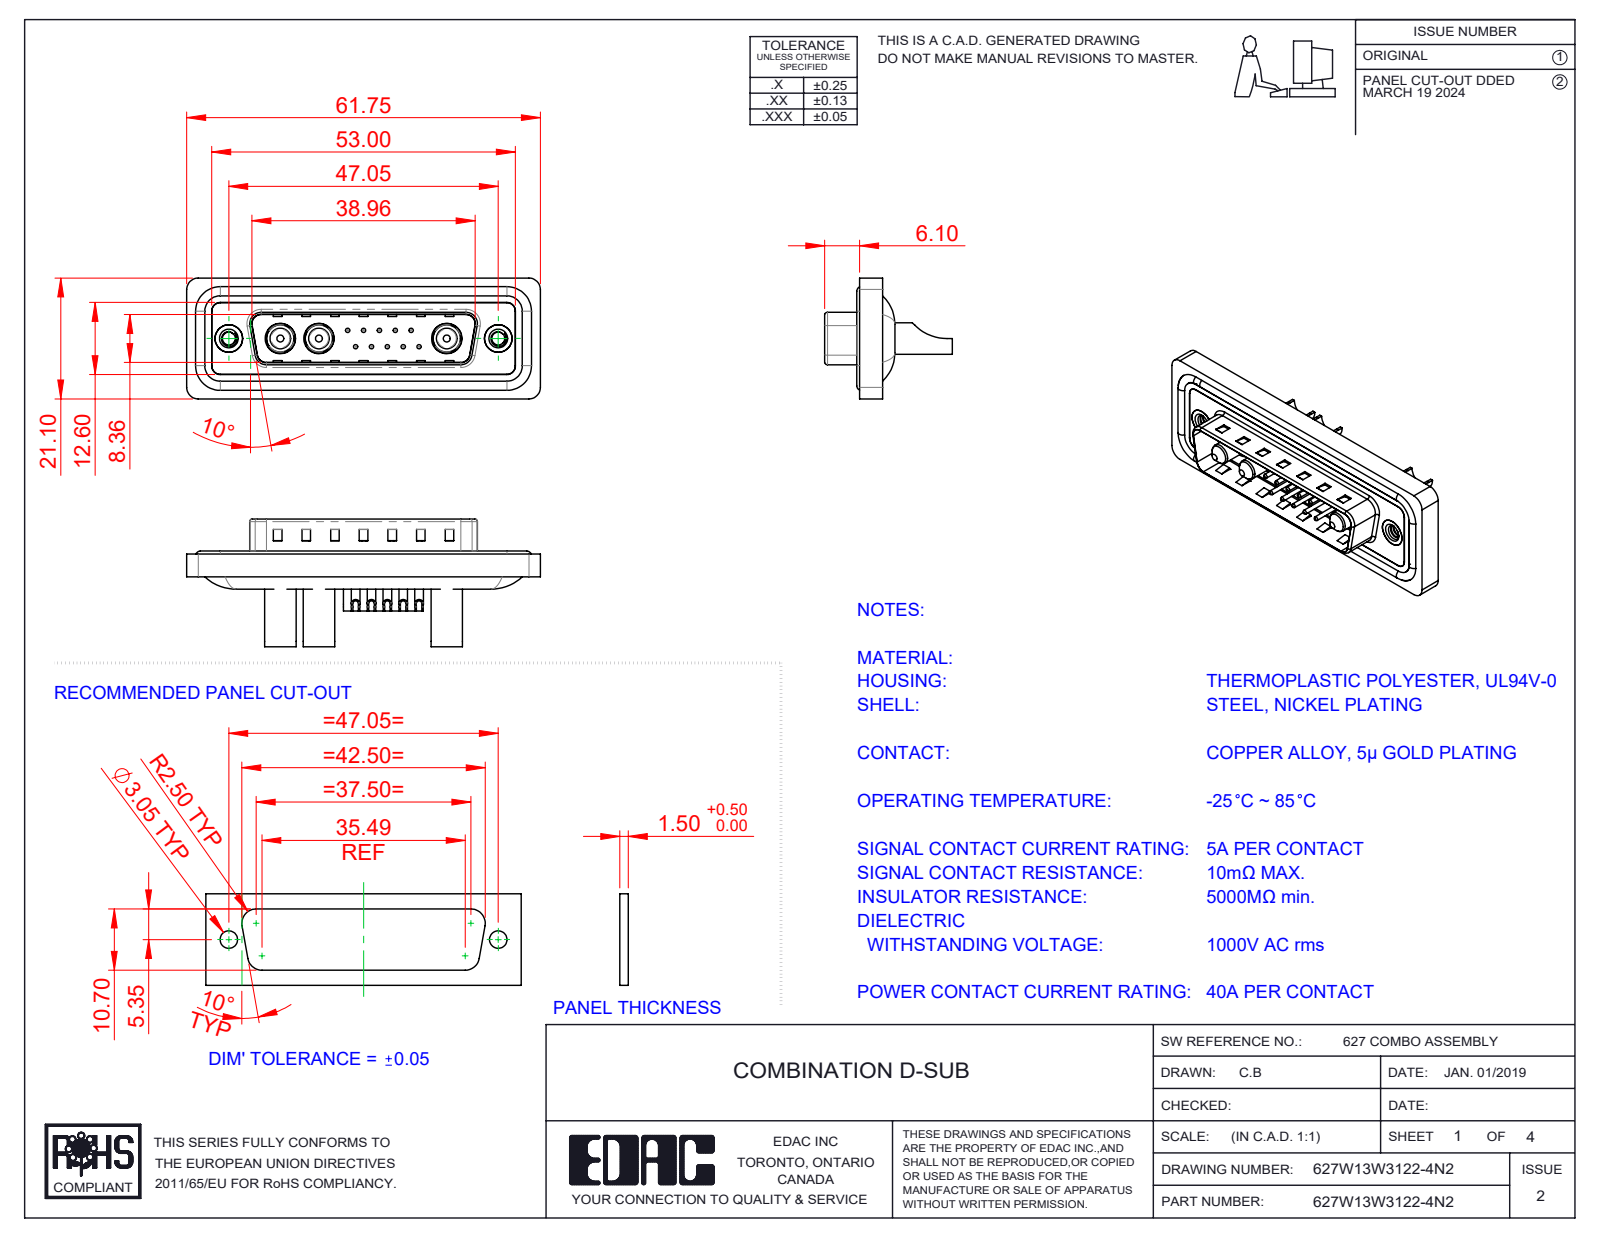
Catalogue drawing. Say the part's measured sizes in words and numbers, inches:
The part is named "627W13W3122-4N2; 627Combo Waterproof Housing_25 Contacts; 627Combo Housing_13W3; Power Pin_40A SC (+5 more)". Its 3-D file was written by "SolidWorks 2023 (CONFIG_CONTROL_DESIGN)". It is 23 solids with 979 faces: 335 planar, 408 cylindrical and 236 other. Overall it measures 2.431 by 0.878 by 0.831 inches. Its volume is 0.456 cubic inches and its surface area 19.18 square inches. Round holes: 10 of diameter 0.03, 10 of diameter 0.039, 10 of diameter 0.063, 10 of diameter 0.079, 3 of diameter 0.181, 3 of diameter 0.191, 3 of diameter 0.209, 2 of diameter 0.089, 2 of diameter 0.157, 2 of diameter 0.189, 2 of diameter 0.197. Round bosses or shafts: 10 of diameter 0.059, 4 of diameter 0.063, 3 of diameter 0.217, 3 of diameter 0.205, 3 of diameter 0.187, 3 of diameter 0.148, 3 of diameter 0.142, 2 of diameter 0.193. Partial cylindrical surfaces (rounded edges, fillets, slot ends): 22 of radius 0.059, 18 of radius 0.079, 8 of radius 0.02, 8 of radius 0.063, 6 of radius 0.039, 4 of radius 0.01, 4 of radius 0.024, 4 of radius 0.026. The main face-to-face distances are 0.016, 0.043, 0.059, 0.063, 0.02, 0.122, 0.114, 0.032, 0.377, 0.161. The hole center spacings are 0.124, 0.109, 0.198, 0.218, 0.295, 0.198, 0.327, 0.398.
